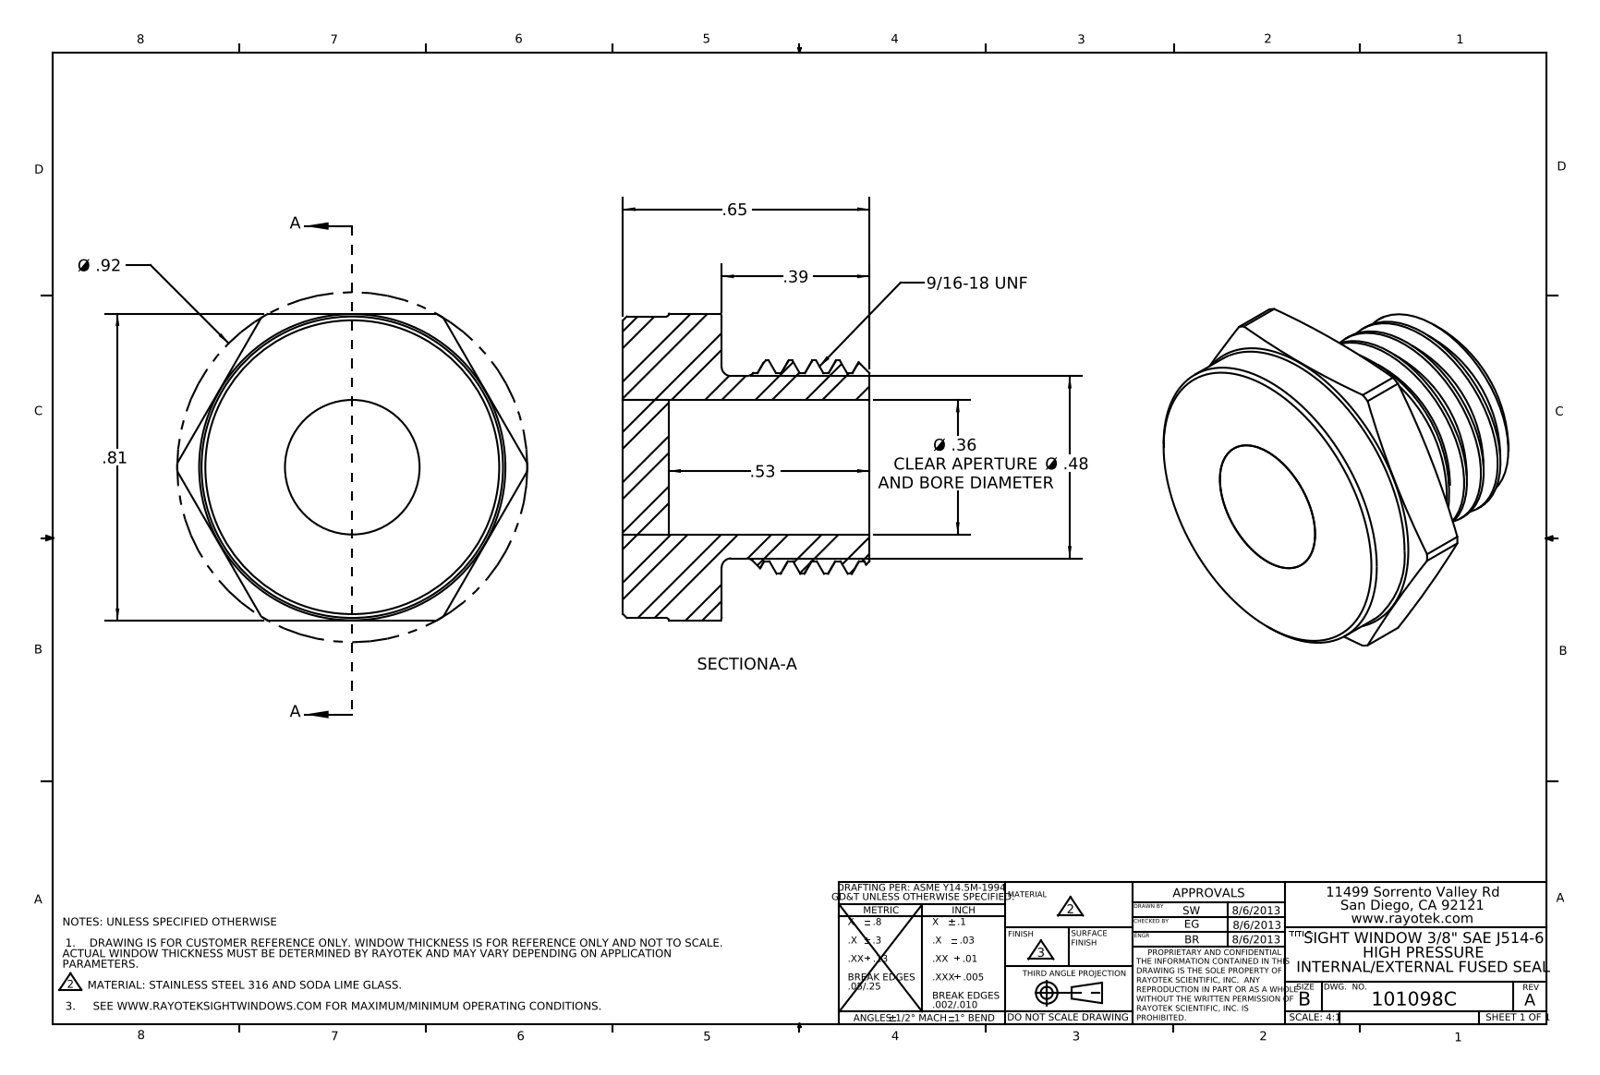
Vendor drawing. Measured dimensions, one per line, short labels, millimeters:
name: 403098
written by: SolidWorks 2012 (AUTOMOTIVE_DESIGN)
unit: mm
bodies: 2 solids, 55 faces (11 planar, 24 cylindrical, 20 other)
size: 23.4 × 20.6 × 16.5
volume: 2 750 mm³; area: 2 298 mm²
holes: 1× ⌀9
bosses: 1× ⌀20.2, 1× ⌀14.3, 1× ⌀12.2
rounds: 1× R11.7
face distances: 6.6, 20.6, 3.6, 3, 9.9, 13.5, 16.5
